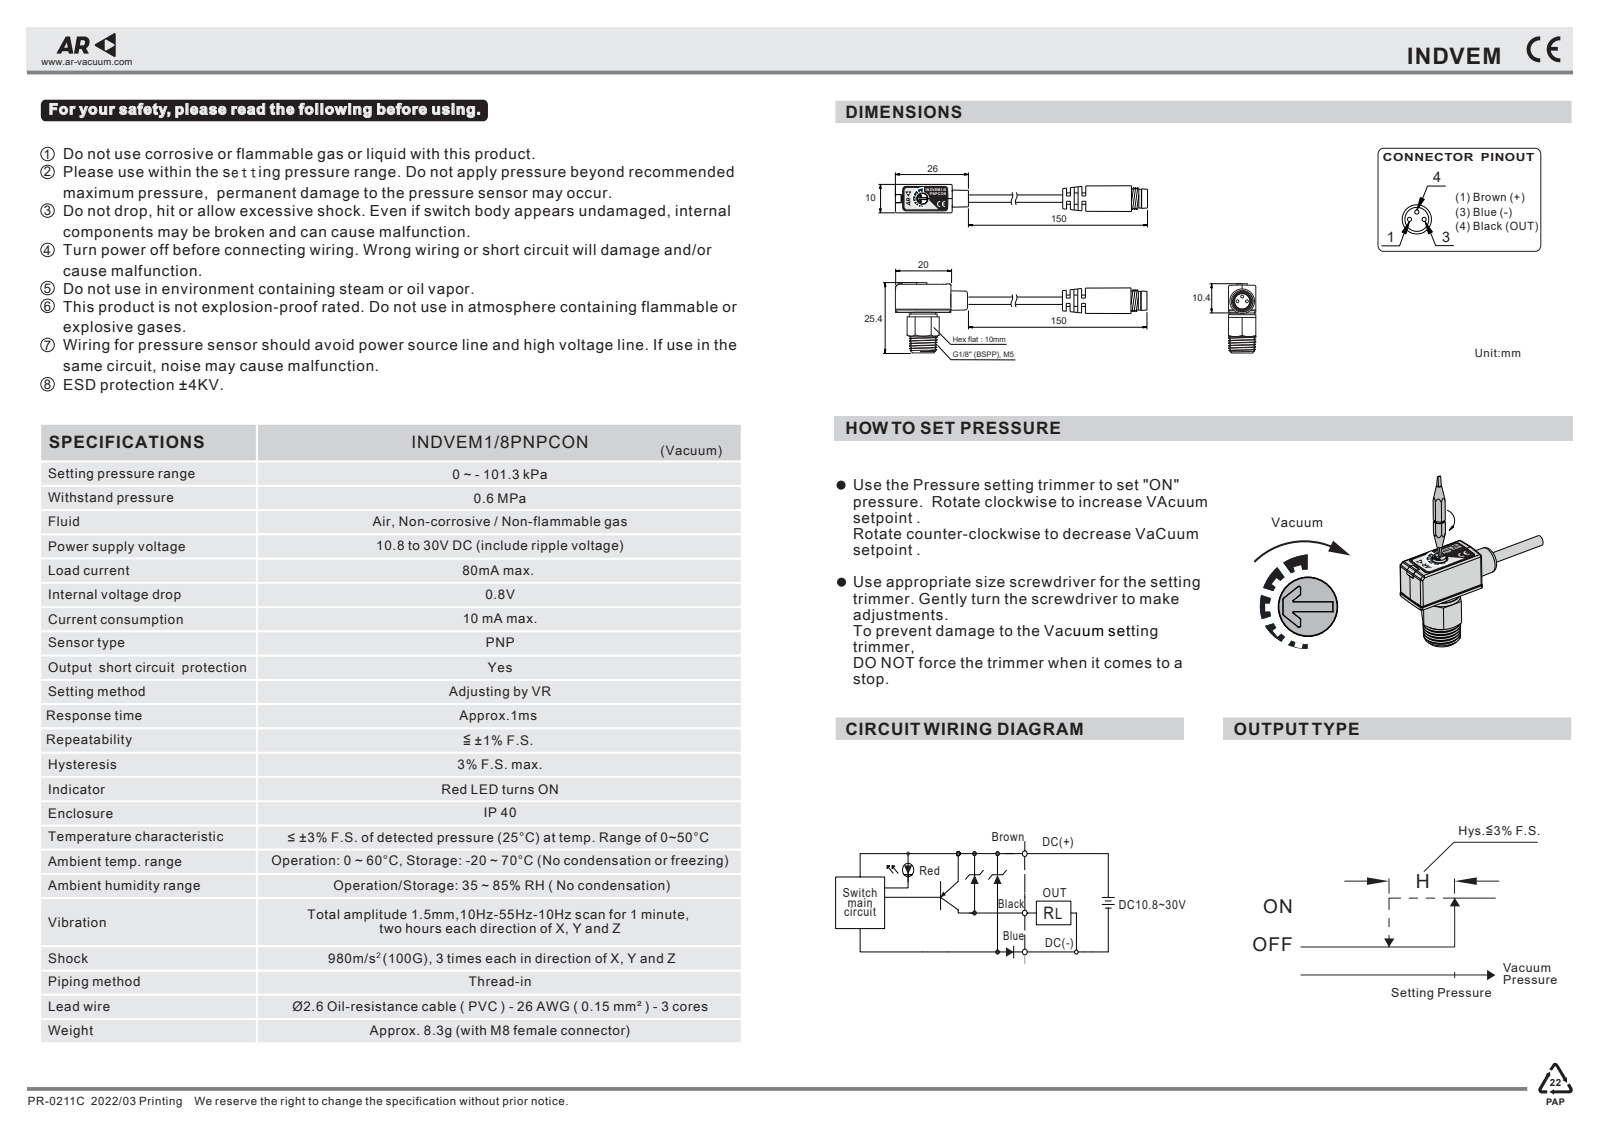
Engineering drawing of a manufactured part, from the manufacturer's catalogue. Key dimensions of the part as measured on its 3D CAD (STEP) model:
Part name (STEP PRODUCT): indvem1-8pnpcon
STEP written by: Autodesk Inventor 2024 (AUTOMOTIVE_DESIGN)
Units: millimetres
Bodies: 1 solid, 32 faces (23 planar, 6 cylindrical, 3 other)
Overall size (bounding box): 180 × 25.4 × 11.52
Volume: 5 280 mm³ · Surface area: 3 331 mm²
Round bosses / shafts (diameter × count): ⌀9 ×1, ⌀7.7 ×1, ⌀7 ×1, ⌀4.5 ×1, ⌀2.5 ×1
Main face-to-face distances: 10, 10.5, 20, 6, 14.2, 24.7, 180, 160, 151, 131
